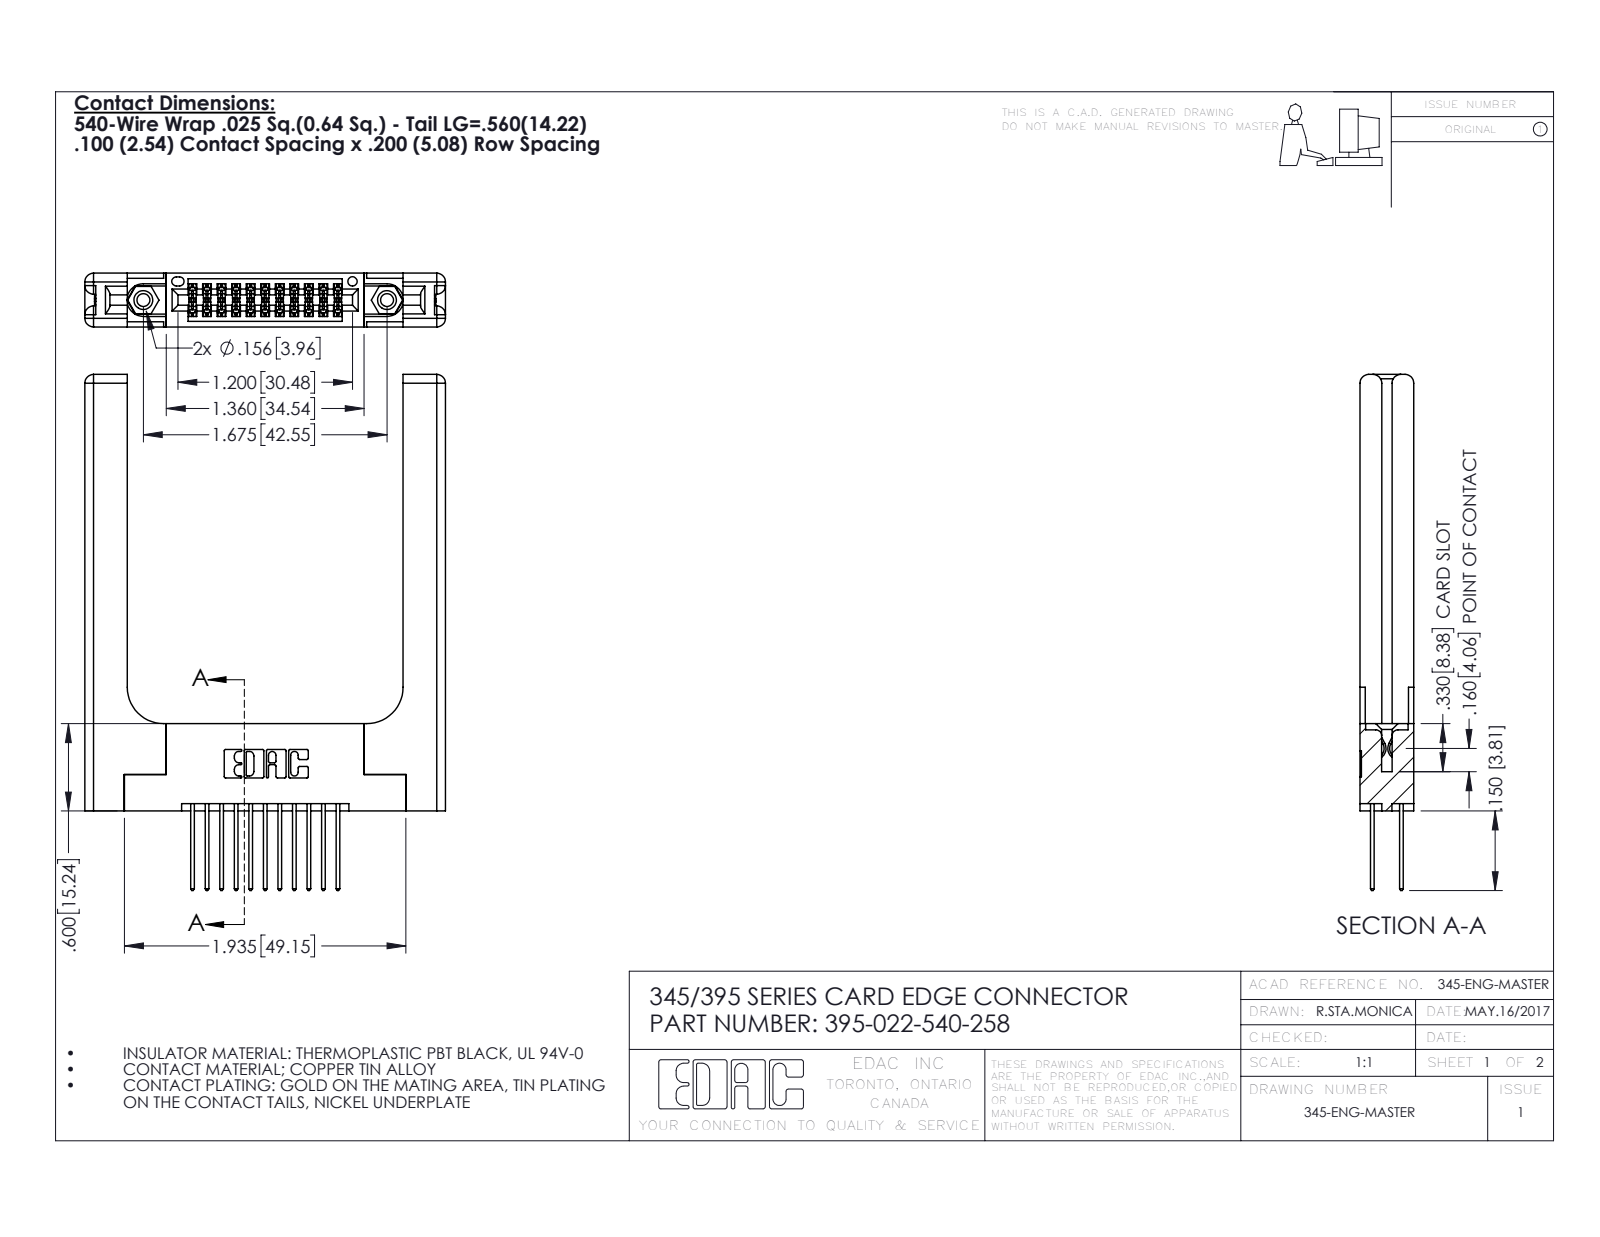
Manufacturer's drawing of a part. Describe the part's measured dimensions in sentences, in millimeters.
The part is named "345 Part_Flush Mounting Lugs - 0.156 Dia-TH; 345-250-001_345-250-001-102; 345-292-001_345-293-140; 395-022-540-258 (+1 more)". Its 3-D file was written by "SolidWorks 2016 (CONFIG_CONTROL_DESIGN)". It is 27 solids with 1482 faces: 954 planar, 468 cylindrical and 60 other. Overall it measures 90.1 by 63 by 9.4 millimeters. Its volume is 14 400 cubic millimeters and its surface area 13 590 square millimeters. Round holes: 2 of diameter 2.3, 2 of diameter 3.2, 2 of diameter 4, 1 of diameter 1.6. Round bosses or shafts: 2 of diameter 3.9. Partial cylindrical surfaces (rounded edges, fillets, slot ends): 33 of radius 0.2, 22 of radius 0.3, 22 of radius 0.3, 16 of radius 1.5, 6 of radius 0.2, 6 of radius 0.8, 3 of radius 0.7, 2 of radius 0.4. The main face-to-face distances are 9.4, 1.8, 7.6, 5.1, 2, 3.8, 3.8, 5.6, 2.5, 6.9. The hole center spacings are 6.9, 36.7, 42.5.
